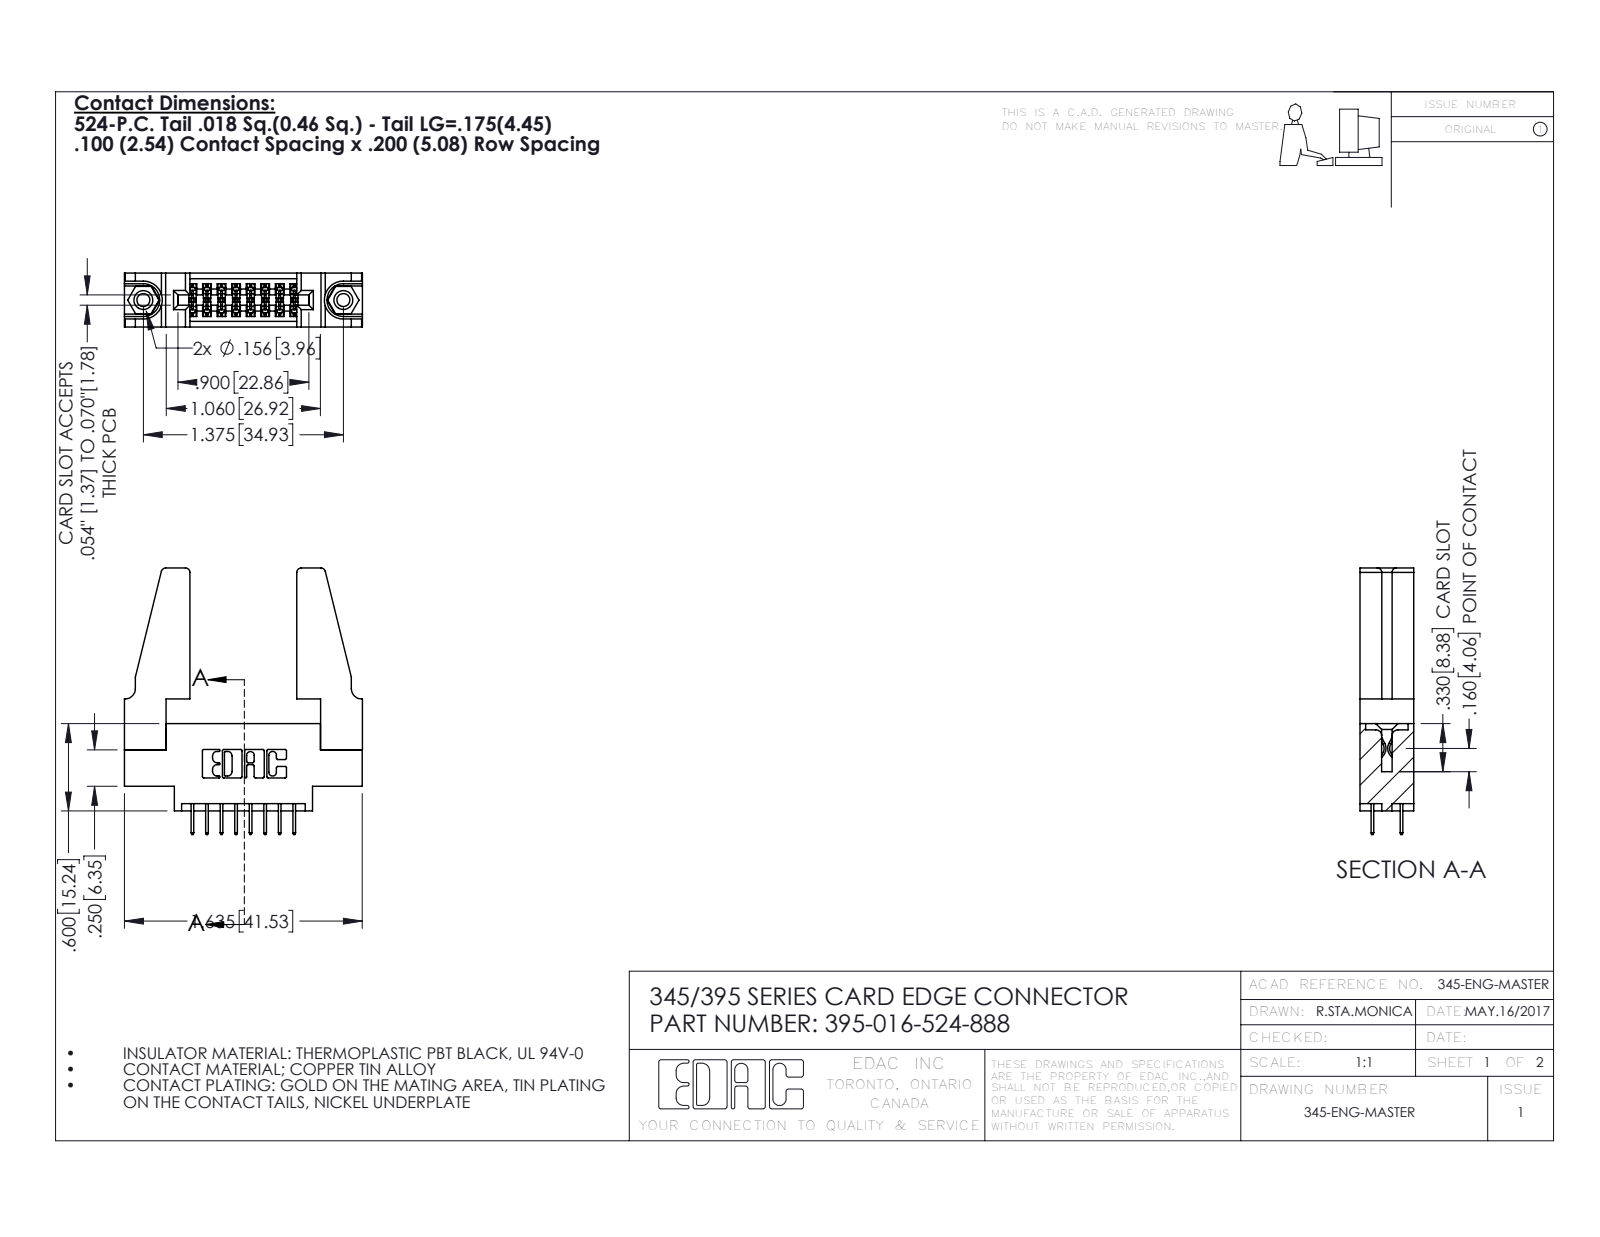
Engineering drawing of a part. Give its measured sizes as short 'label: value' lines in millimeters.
name: 345 Part_0.170 Offset - 0.156 Dia-TH; 345-250-001_345-250-001-102; 395-016-524-888; 345-220-078_345-220-088 (+1 more)
written by: SolidWorks 2016 (CONFIG_CONTROL_DESIGN)
unit: mm
bodies: 21 solids, 1118 faces (780 planar, 322 cylindrical, 16 other)
size: 46.5 × 41.6 × 9.4
volume: 6 830 mm³; area: 7 839 mm²
holes: 2× ⌀2.3, 2× ⌀3.2, 2× ⌀4, 1× ⌀1.6
bosses: 2× ⌀3.9
rounds: 24× R0.2, 22× R0.3, 8× R0.8, 6× R0.2, 6× R0.8, 3× R0.7, 2× R0.4, 2× R0.5
face distances: 9.4, 1.8, 7.6, 5.1, 5.7, 2.5, 6.9, 0.6, 3.8, 3.8
hole spacings: 6.9, 29.1, 34.9
